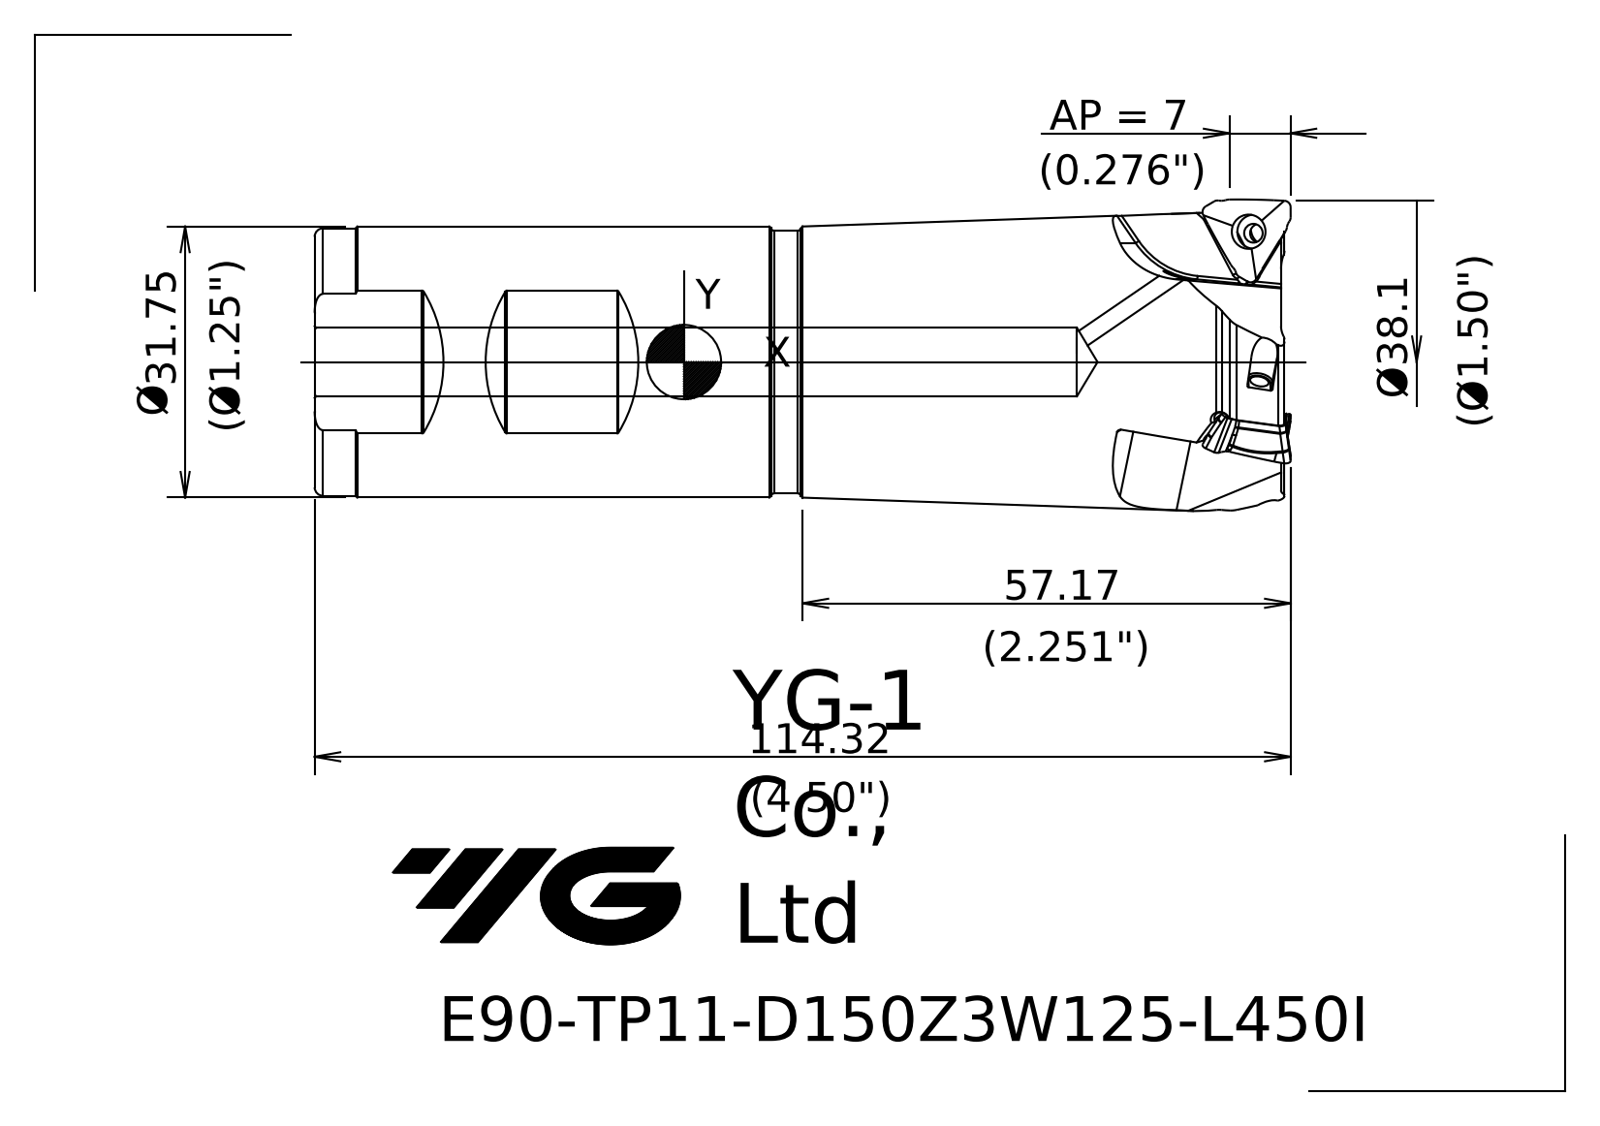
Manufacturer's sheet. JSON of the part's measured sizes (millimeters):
{"part_name": "10222DA0A397nvkn", "step_written_by": "SIEMENS PLM Software NX 10.0 (AP203_CONFIGURATION_CONTROLLED_3D_DESIGN_OF_MECHANICAL_PARTS_AND_ASSEMBLIES_MIM_LF)", "units": "millimeters", "bodies": {"solids": 1, "faces": 58, "planar": 8, "cylindrical": 8, "other": 42}, "overall_size": [114.32, 38.19, 38.19], "volume_mm3": 89940, "surface_area_mm2": 18762, "round_holes": [[1.5, 1], [8, 1]], "round_bosses_or_shafts": [[31.75, 1], [31.35, 1], [30.75, 1]], "partial_cylinders_radius": [[0.3, 3]], "face_to_face_distances": [113.2, 16.14, 0.4, 113.6]}
